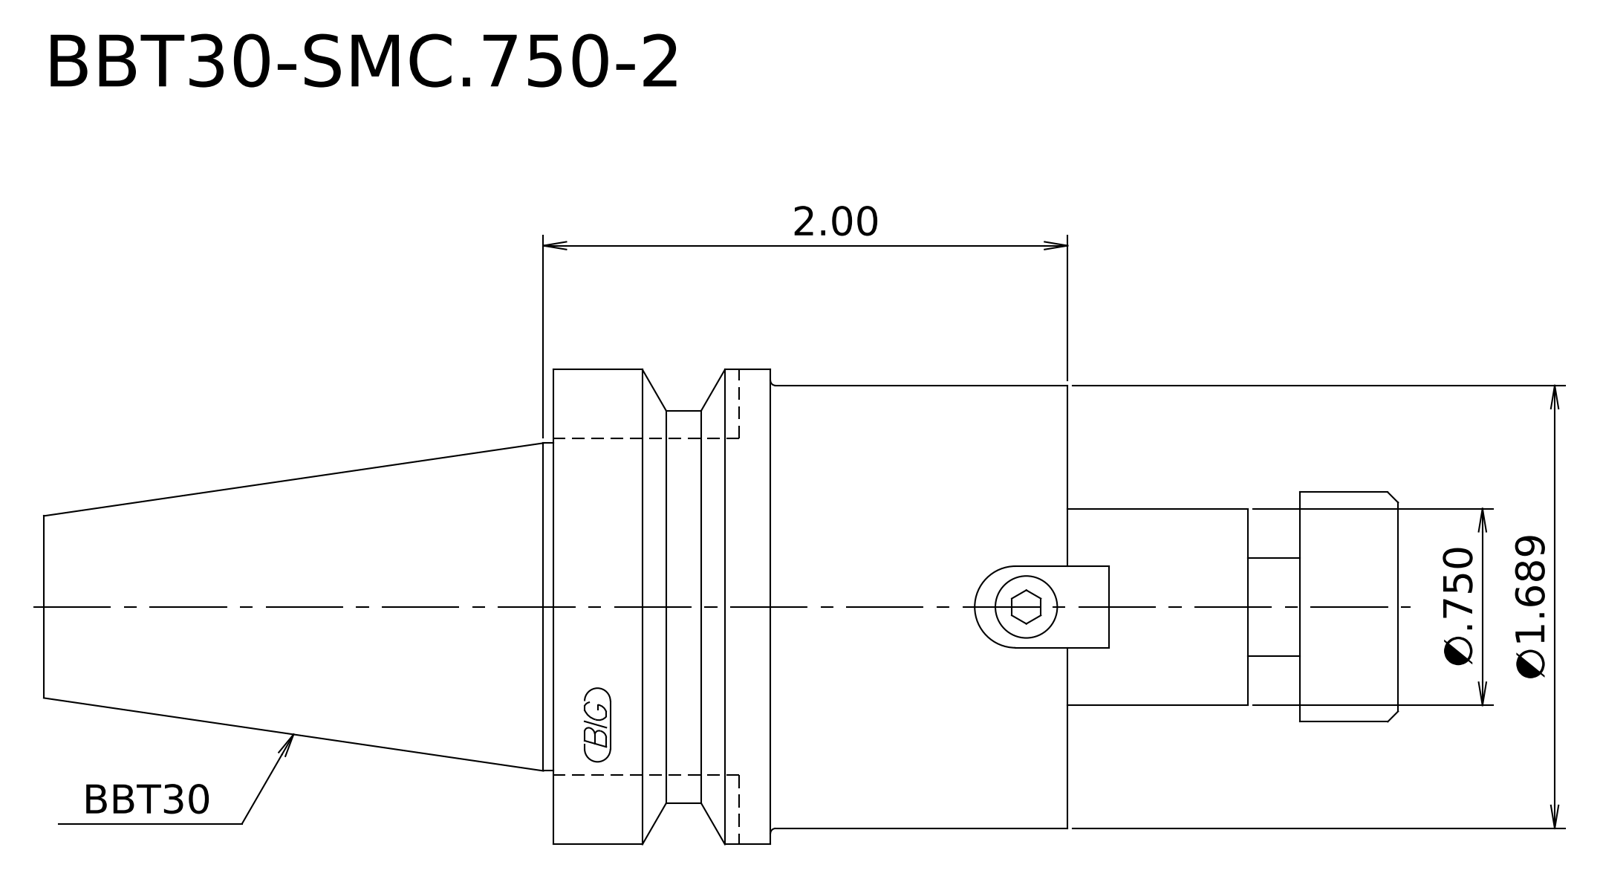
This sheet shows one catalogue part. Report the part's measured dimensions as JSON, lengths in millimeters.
{"part_name": "BBT30-SMC_750-2", "step_written_by": "SolidWorks 2021 (CONFIG_CONTROL_DESIGN)", "units": "millimeters", "bodies": {"solids": 1, "faces": 26, "planar": 17, "cylindrical": 6, "other": 3}, "overall_size": [103.16, 46, 46], "volume_mm3": 96958, "surface_area_mm2": 15121, "round_holes": [[8.43, 1]], "round_bosses_or_shafts": [[46, 1], [42.9, 1], [38, 1], [31.75, 1]], "face_to_face_distances": [49.8, 28.8, 21, 99.2, 70.4, 49.4, 3.96, 32.76, 53.76, 103.16]}
